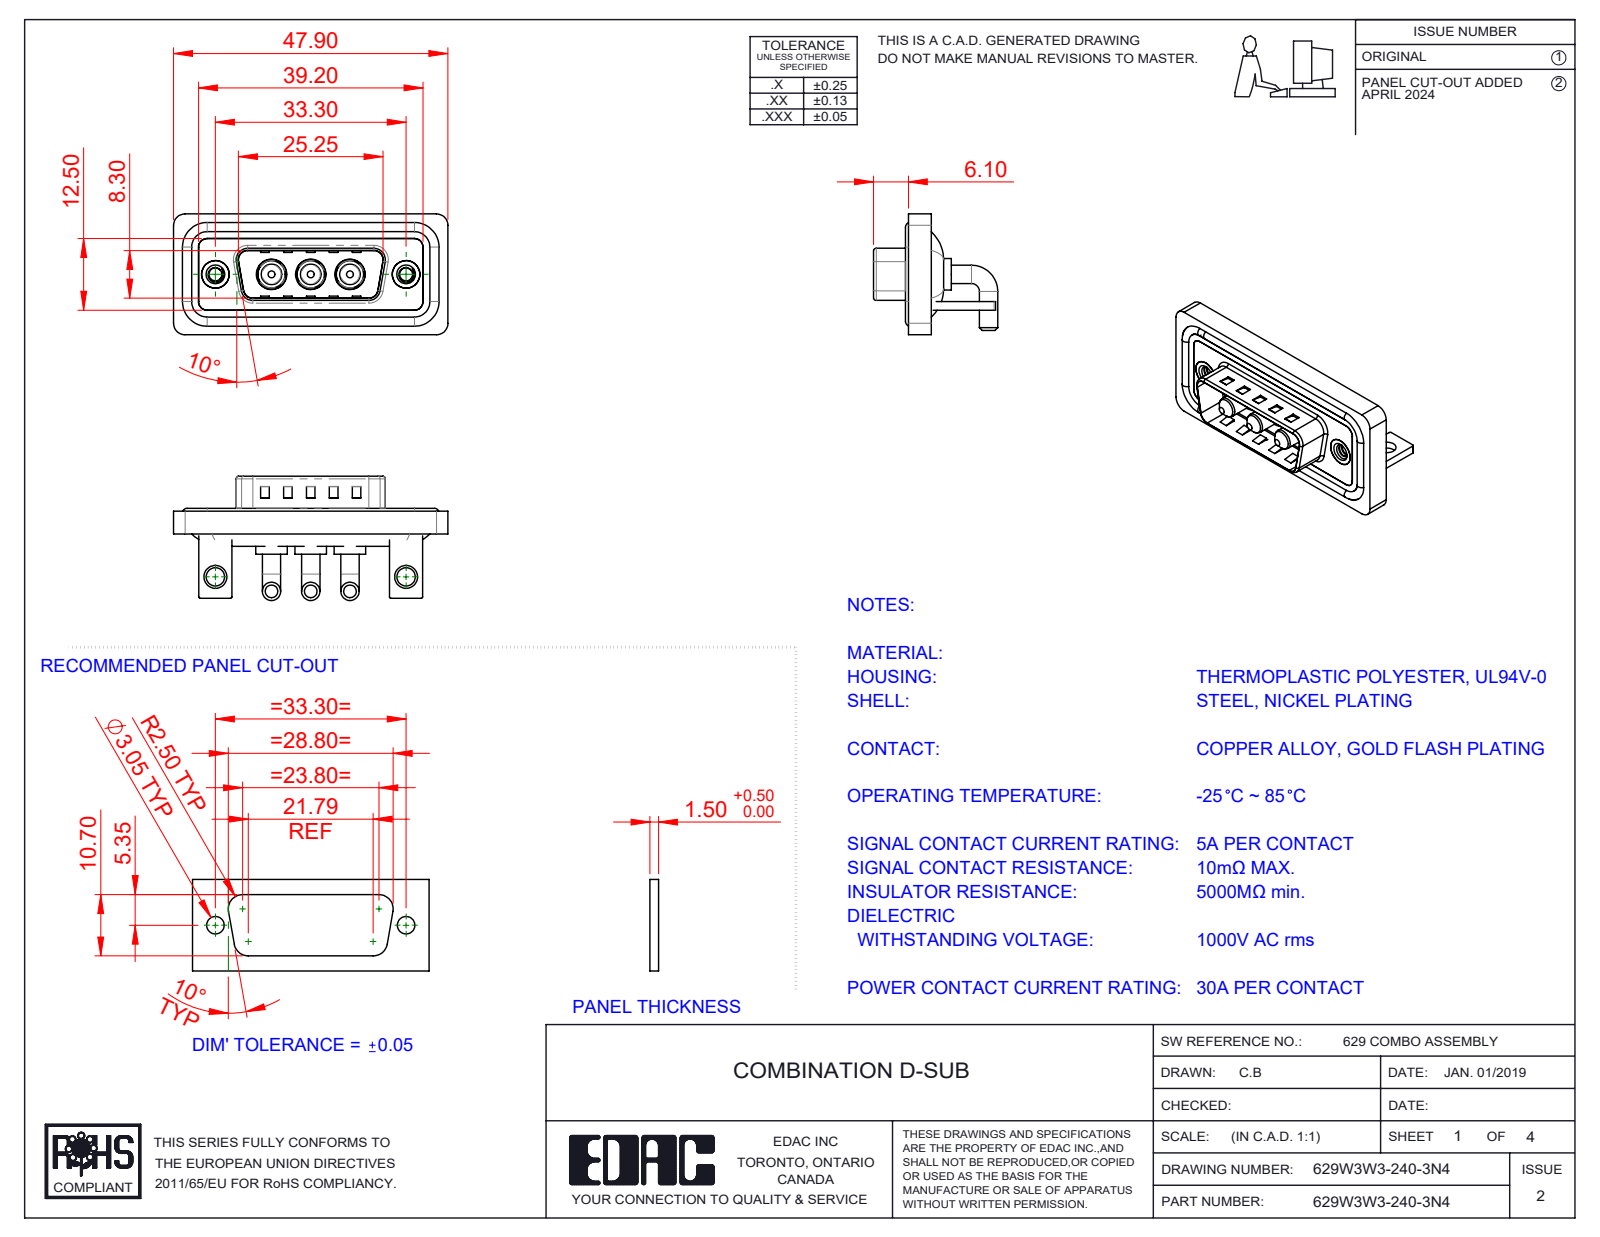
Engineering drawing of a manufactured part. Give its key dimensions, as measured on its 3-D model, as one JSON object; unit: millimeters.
{"part_name": "Power Pin_30A RA; 629Combo Shell Rear_15 Contacts; 629Combo Stabilizer Bracket; 629Combo Shell Front_15 Contacts (+4 more)", "step_written_by": "SolidWorks 2023 (CONFIG_CONTROL_DESIGN)", "units": "millimeters", "bodies": {"solids": 15, "faces": 616, "planar": 227, "cylindrical": 265, "other": 124}, "overall_size": [47.9, 21.7, 21.1], "volume_mm3": 6140, "surface_area_mm2": 9678, "round_holes": [[4.85, 3], [5.3, 3], [2.26, 2], [3.2, 2], [4, 2], [4.8, 2], [5, 2]], "round_bosses_or_shafts": [[3.2, 6], [1.6, 4], [5.5, 3], [5.2, 3], [4.75, 3], [3.75, 3], [3.6, 3], [4.9, 2]], "partial_cylinders_radius": [[2, 21], [1.5, 18], [0.25, 16], [0.5, 9], [1.6, 8], [0.6, 4], [0.65, 4], [0.9, 4]], "face_to_face_distances": [0.4, 1.5, 0.8, 2.9, 1.1, 2.1, 3.7, 1.6, 1.2, 4.5], "hole_center_spacings": [6.85, 9.8, 16.65, 23.5, 33.3, 13.7]}
